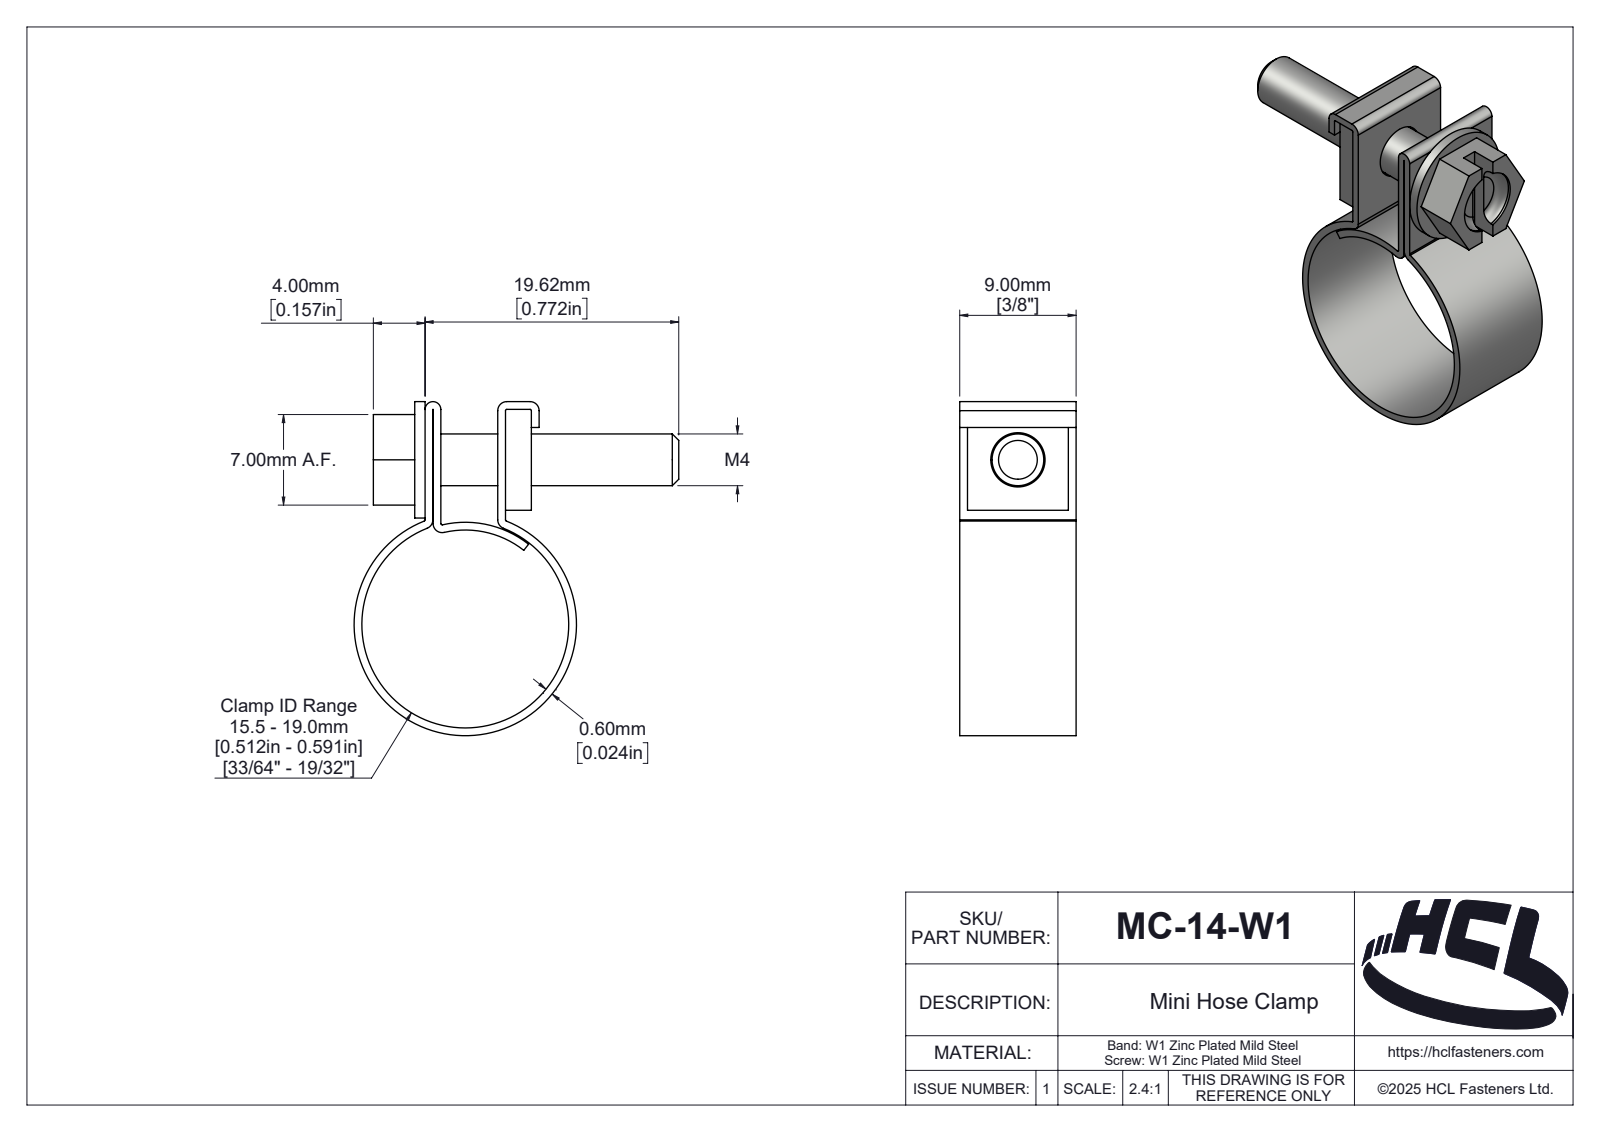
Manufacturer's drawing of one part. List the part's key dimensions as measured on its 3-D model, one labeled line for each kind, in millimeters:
Part name (STEP PRODUCT): MC-14-W1
STEP written by: SolidWorks 2025 (AUTOMOTIVE_DESIGN)
Units: millimetres
Bodies: 3 solids, 175 faces (38 planar, 84 cylindrical, 53 other)
Overall size (bounding box): 25.83 × 25.11 × 9
Volume: 933 mm³ · Surface area: 2 271 mm²
Round holes (diameter × count): ⌀4.2 ×1, ⌀5 ×1, ⌀16 ×1
Round bosses / shafts (diameter × count): ⌀17.2 ×1, ⌀9 ×1, ⌀4 ×1
Partial cylindrical surfaces — rounded edges, fillets, slot ends (radius × count): R0.1 ×5, R0.7 ×5, R0.2 ×1, R0.61 ×1, R0.81 ×1, R1.01 ×1, R1.06 ×1, R1.28 ×1
Main face-to-face distances: 0.6, 0.62, 5, 5.62, 6.22, 7, 2, 2.6, 8.22, 7.6
